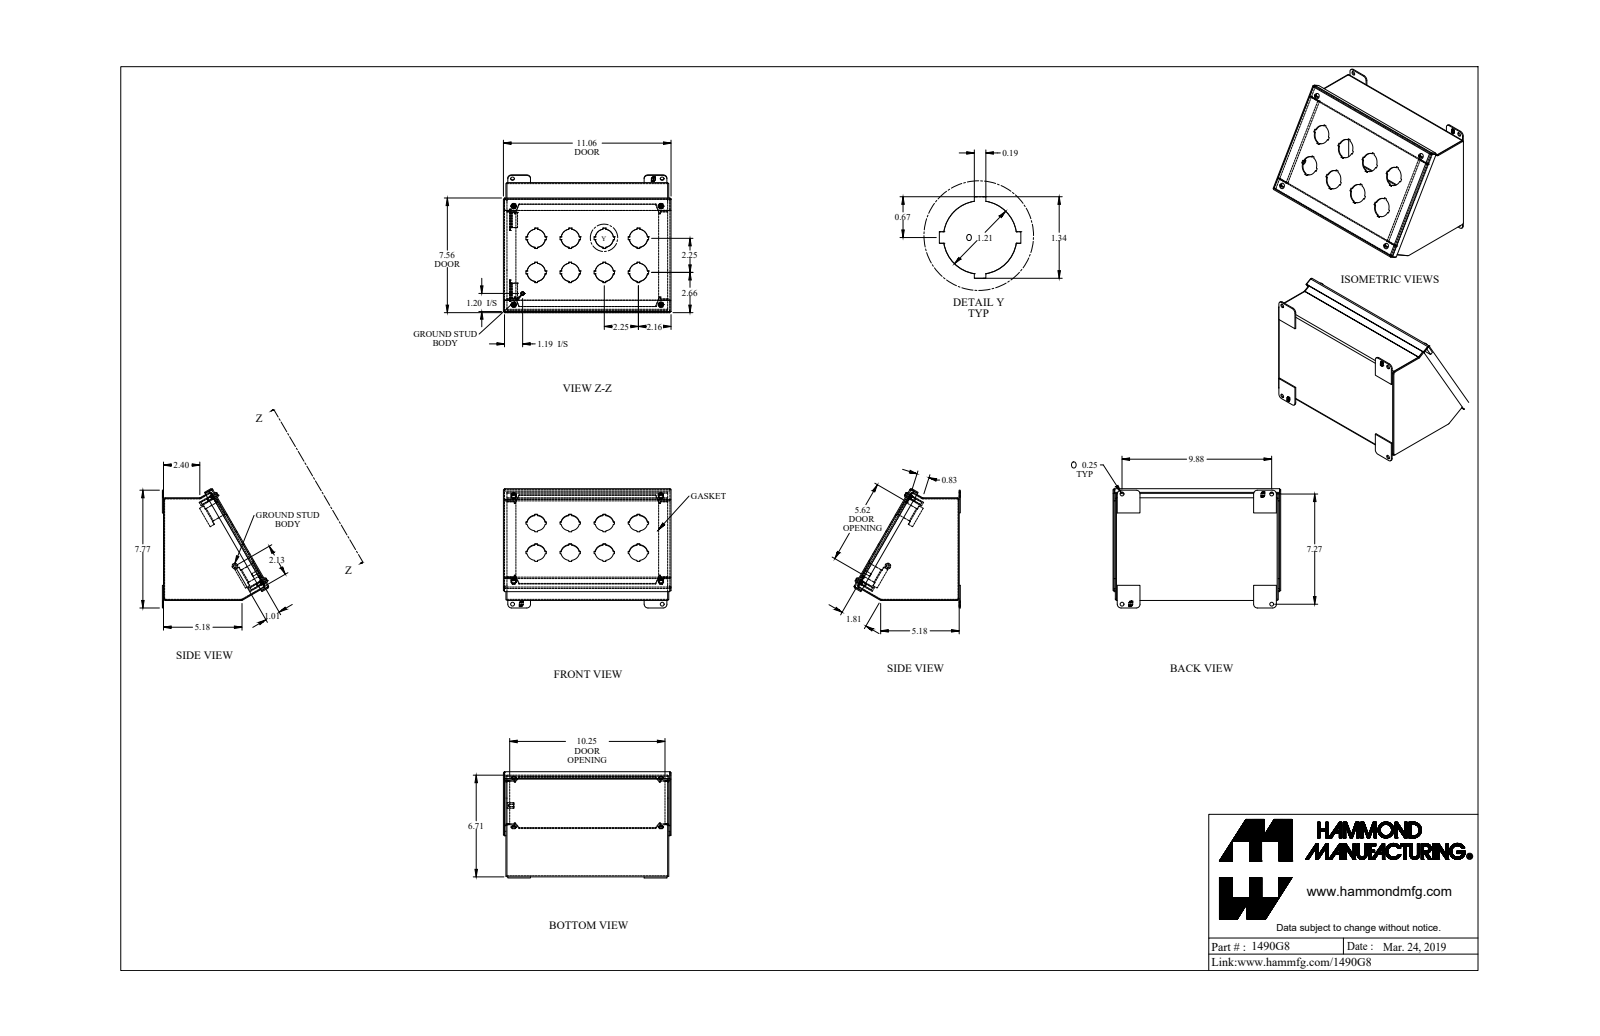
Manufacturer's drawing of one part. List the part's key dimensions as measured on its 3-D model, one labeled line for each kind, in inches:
Part name (STEP PRODUCT): 1490G8_Default
STEP written by: SolidWorks 2019 (CONFIG_CONTROL_DESIGN)
Units: inches
Bodies: 28 solids, 837 faces (601 planar, 196 cylindrical, 40 other)
Overall size (bounding box): 11.062 × 7.869 × 7.008
Volume: 30.65 in³ · Surface area: 804.7 in²
Round holes (diameter × count): ⌀0.25 ×8, ⌀1.21 ×8, ⌀0.159 ×4, ⌀0.156 ×1
Round bosses / shafts (diameter × count): ⌀0.39 ×4, ⌀0.275 ×4, ⌀0.19 ×4, ⌀0.148 ×4, ⌀0.375 ×1, ⌀0.25 ×1, ⌀0.188 ×1
Partial cylindrical surfaces — rounded edges, fillets, slot ends (radius × count): R0.108 ×18, R0.036 ×12, R0.25 ×8, R0.029 ×7, R0.086 ×7, R0.125 ×4, R0.16 ×4, R0.171 ×4
Main face-to-face distances: 0.072, 10.678, 6.697, 10.606, 10.75, 0.259, 0.187, 6.769, 6.625, 7.337
Hole centre spacings: 2.25, 3.182, 4.293, 4.619, 5.749, 6.346, 7.409, 8.5
